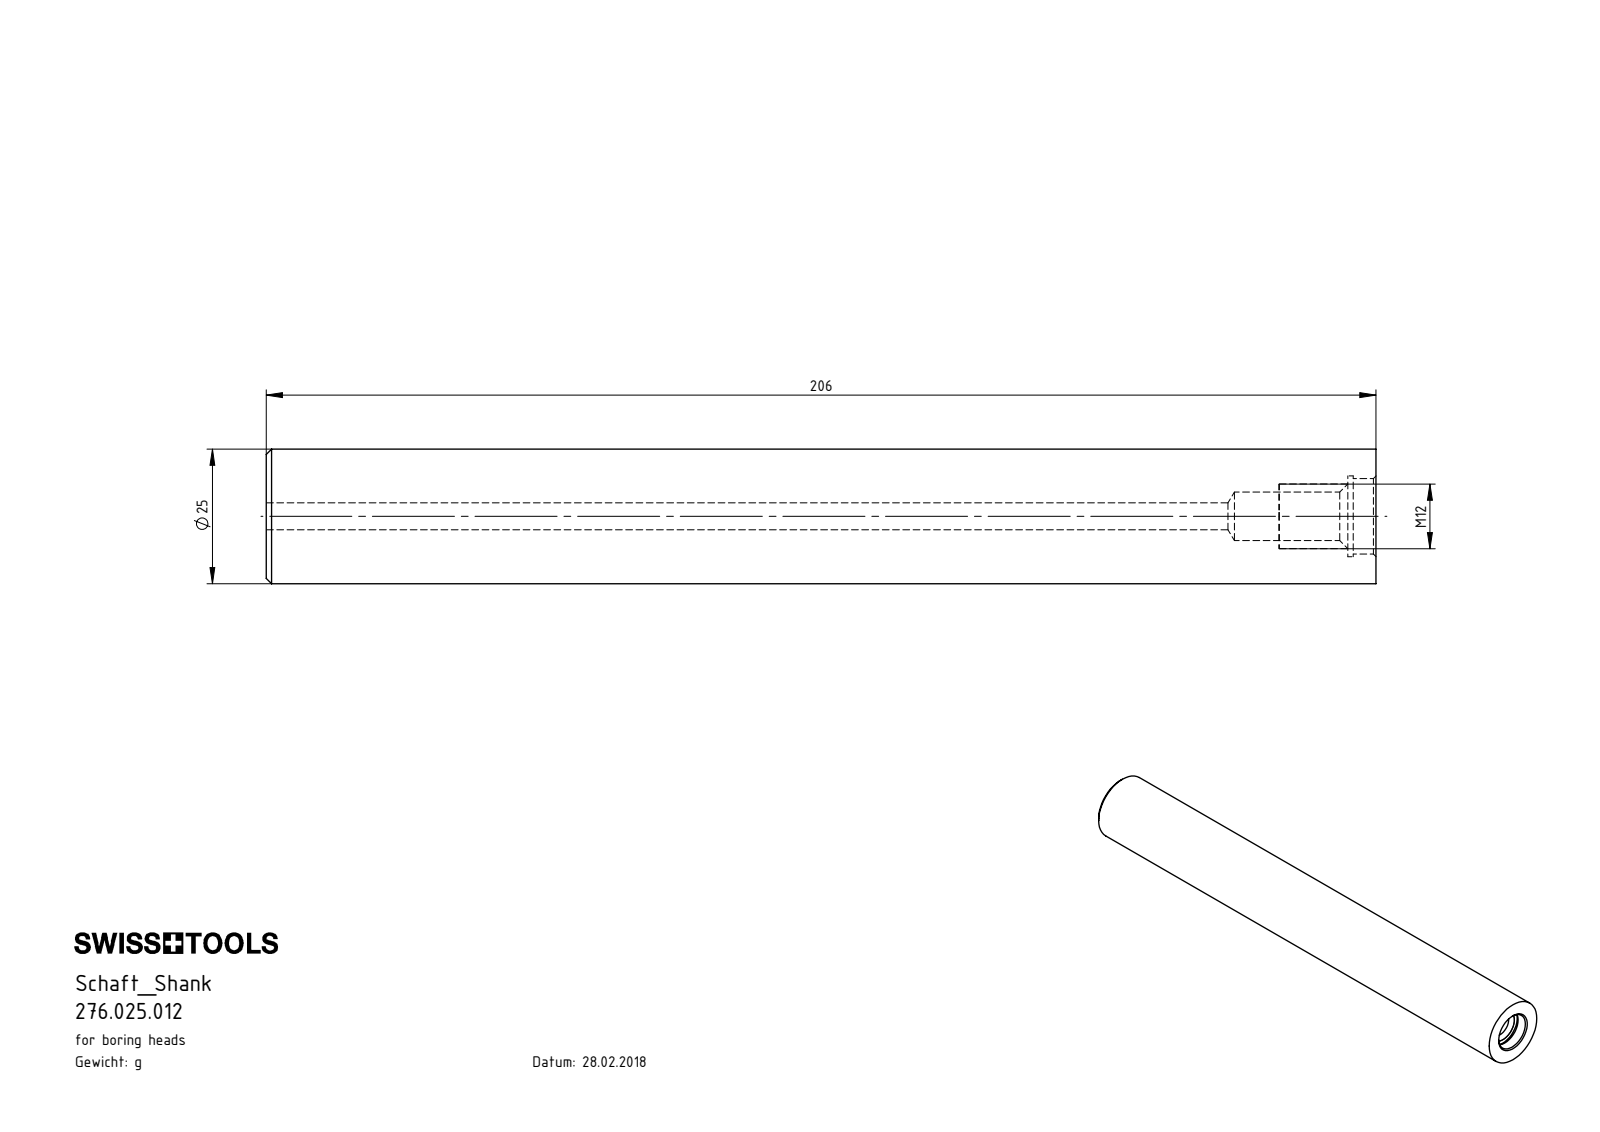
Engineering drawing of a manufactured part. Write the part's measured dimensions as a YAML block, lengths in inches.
part_name: "276.025.012"
step_written_by: "SolidWorks 2017 (CONFIG_CONTROL_DESIGN)"
units: inches
bodies: {solids: 1, faces: 22, planar: 4, cylindrical: 10, other: 8}
overall_size: [8.11, 0.984, 0.984]
volume: 5.817
surface_area: 32.13
round_holes:
  - {diameter: 0.197, count: 1}
  - {diameter: 0.354, count: 1}
  - {diameter: 0.551, count: 1}
  - {diameter: 0.591, count: 1}
round_bosses_or_shafts:
  - {diameter: 0.984, count: 1}
face_to_face_distances: [8.11, 7.904, 0.207, 7.943, 0.039, 0.167]
